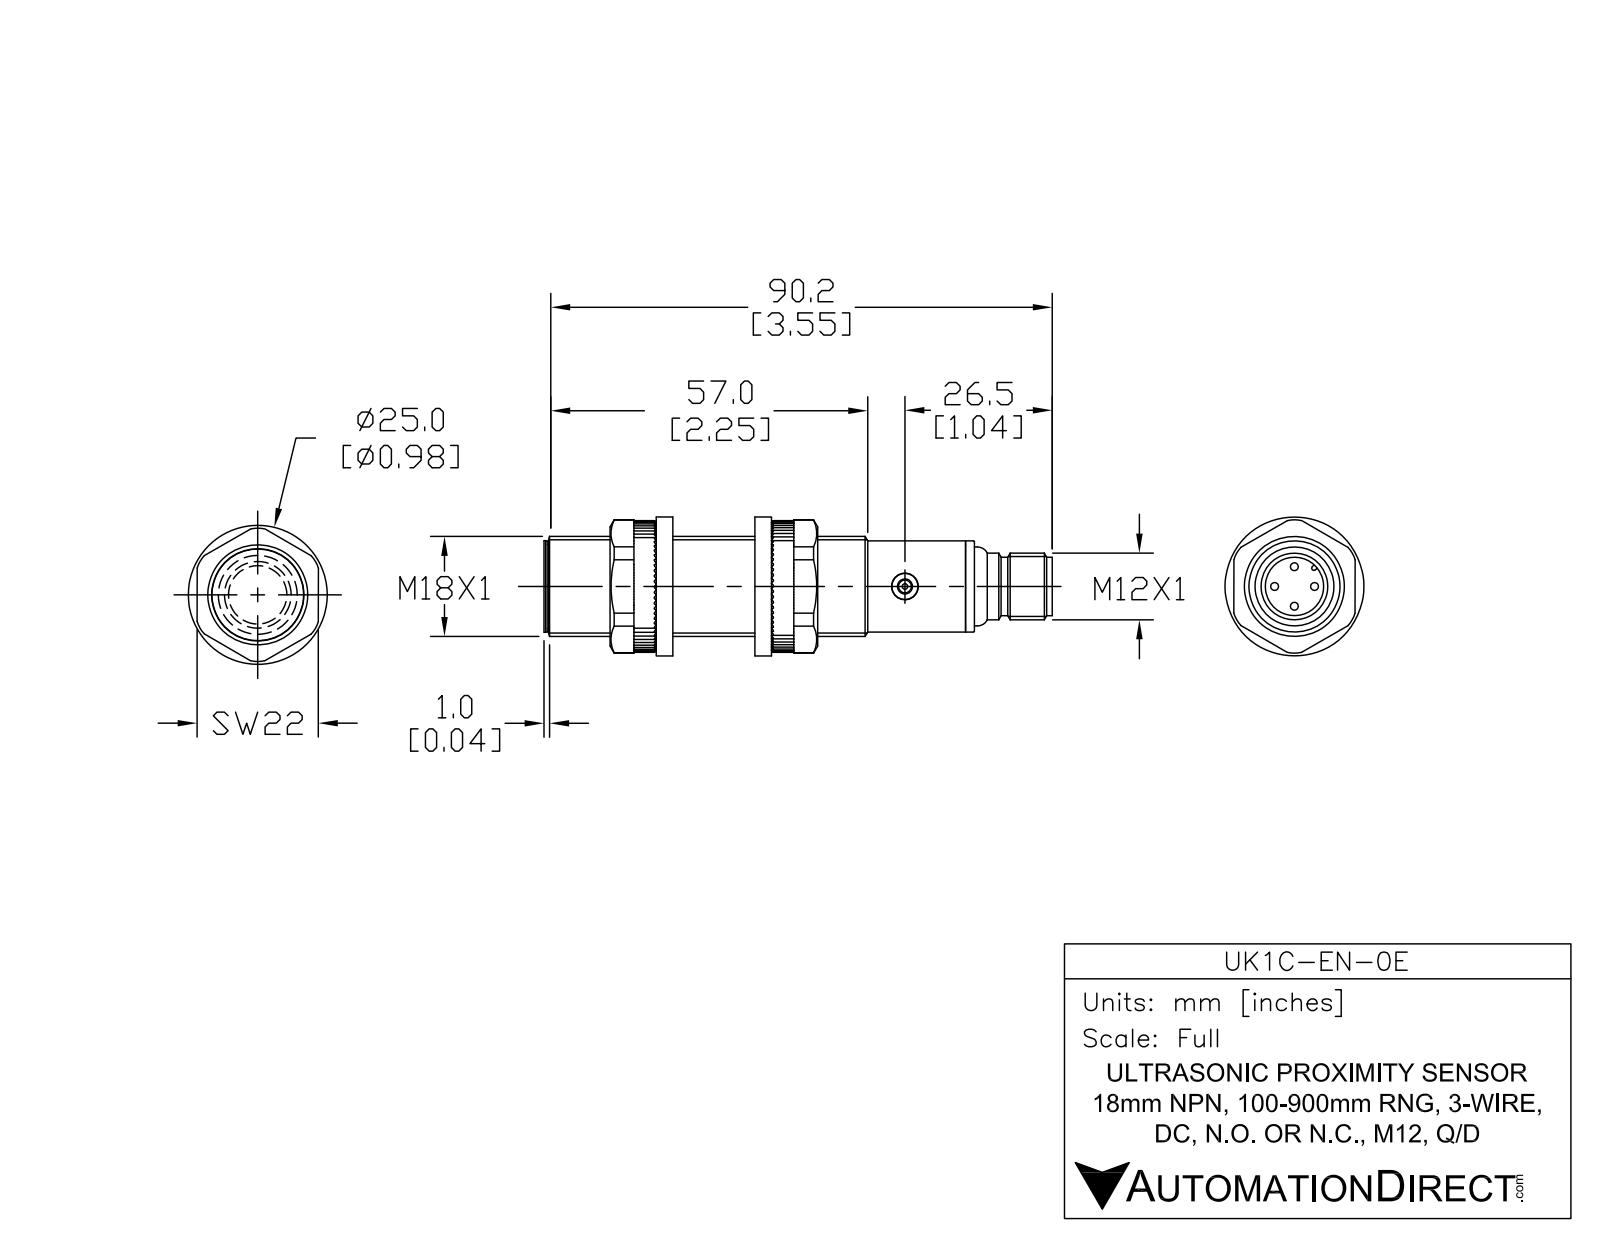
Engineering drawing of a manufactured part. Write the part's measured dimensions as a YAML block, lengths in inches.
part_name: "UK1C-EN-0E"
step_written_by: "SolidWorks 2017 (AUTOMOTIVE_DESIGN)"
units: inches
bodies: {solids: 6, faces: 106, planar: 21, cylindrical: 48, other: 37}
overall_size: [3.606, 0.709, 0.709]
volume: 1.202
surface_area: 10.68
round_holes:
  - {diameter: 0.106, count: 1}
  - {diameter: 0.185, count: 1}
  - {diameter: 0.276, count: 1}
  - {diameter: 0.327, count: 1}
  - {diameter: 0.374, count: 1}
round_bosses_or_shafts:
  - {diameter: 0.039, count: 4}
  - {diameter: 0.709, count: 1}
  - {diameter: 0.654, count: 1}
  - {diameter: 0.646, count: 1}
  - {diameter: 0.622, count: 1}
  - {diameter: 0.559, count: 1}
  - {diameter: 0.472, count: 1}
  - {diameter: 0.413, count: 1}
partial_cylinders:
  - {radius: 0.024, count: 1}
face_to_face_distances: [2.957, 0.039, 2.996, 0.037, 2.994, 0.043, 0.157, 3.055, 3.053, 3.016]
